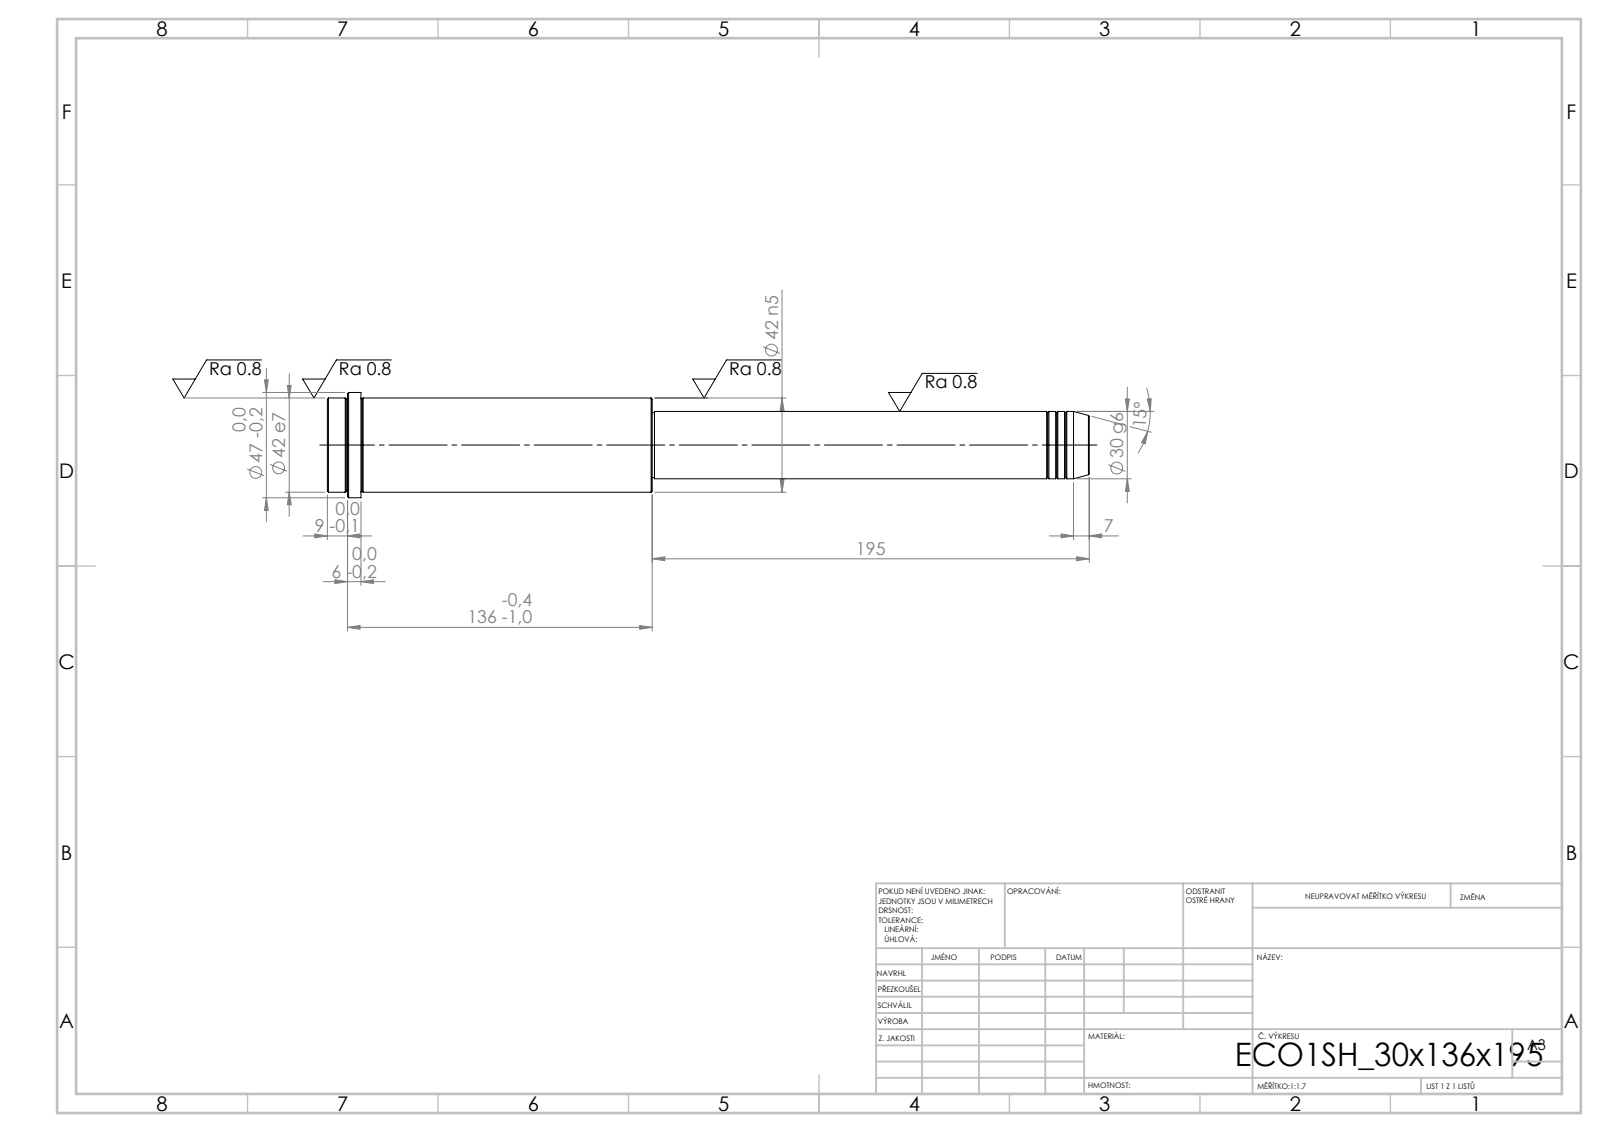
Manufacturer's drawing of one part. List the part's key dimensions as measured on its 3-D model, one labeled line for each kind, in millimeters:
STEP written by: SolidWorks 2019 (CONFIG_CONTROL_DESIGN)
Units: millimetres
Bodies: 1 solid, 52 faces (6 planar, 16 cylindrical, 30 other)
Overall size (bounding box): 340 × 47 × 47
Volume: 339 919 mm³ · Surface area: 41 145 mm²
Round bosses / shafts (diameter × count): ⌀47 ×1, ⌀42 ×1, ⌀30 ×1, ⌀29 ×1
Main face-to-face distances: 145, 195, 340, 325, 130, 15, 331, 136, 6, 9
